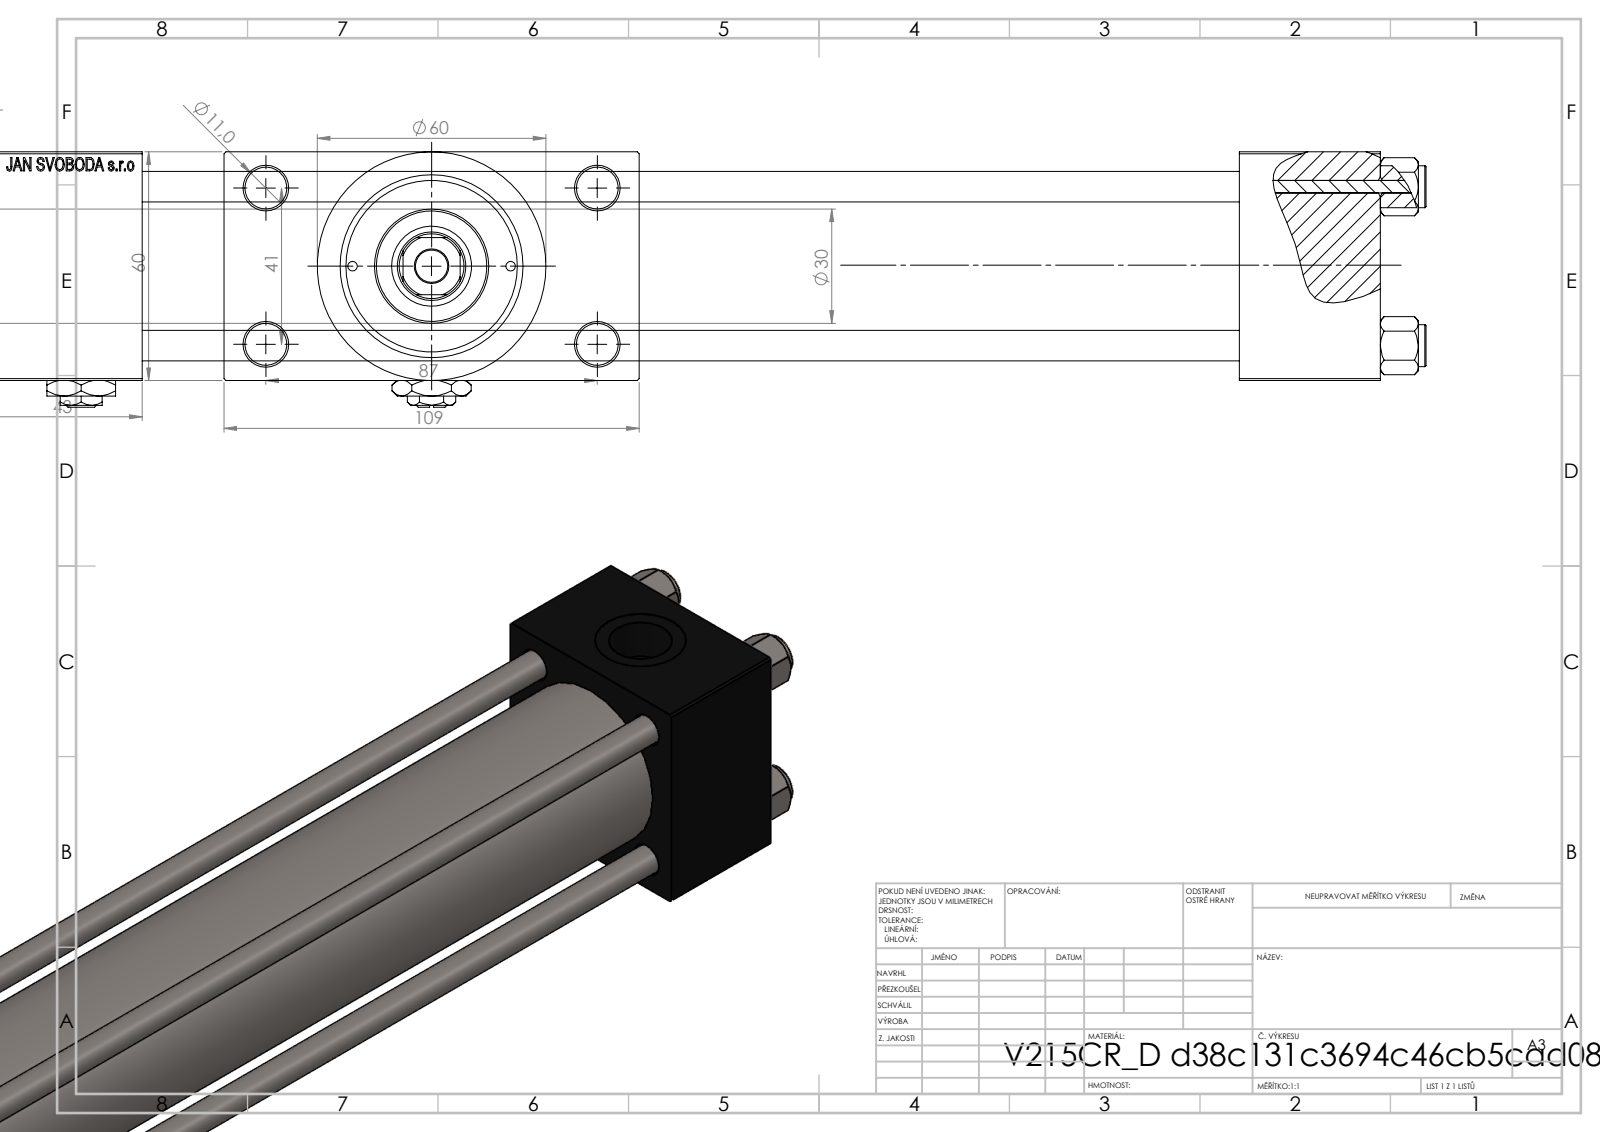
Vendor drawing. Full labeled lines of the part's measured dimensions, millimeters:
Part name (STEP PRODUCT): V215CR_D_TYCINKA; V215CR_VCP_D; NUT_M5_D; Zatka_pro_OIL_PORT (+2 more)
STEP written by: SolidWorks 2019 (CONFIG_CONTROL_DESIGN)
Units: millimetres
Bodies: 12 solids, 1161 faces (524 planar, 97 cylindrical, 540 other)
Overall size (bounding box): 415 × 109 × 67
Volume: 715 104 mm³ · Surface area: 220 405 mm²
Round holes (diameter × count): ⌀8 ×4, ⌀11 ×4, ⌀2.5 ×2, ⌀7 ×2, ⌀16.66 ×2, ⌀24 ×2, ⌀8.5 ×1, ⌀18 ×1, ⌀21 ×1, ⌀31 ×1, ⌀40 ×1, ⌀45 ×1
Round bosses / shafts (diameter × count): ⌀11 ×4, ⌀60 ×1, ⌀46 ×1, ⌀30 ×1
Partial cylindrical surfaces — rounded edges, fillets, slot ends (radius × count): R8.5 ×1
Main face-to-face distances: 60, 24.5, 84.5, 288, 37, 325, 43, 368, 331, 109
Hole centre spacings: 20.85, 22.65, 29.49, 30.62, 41.7, 46.53, 47.15, 48.09
